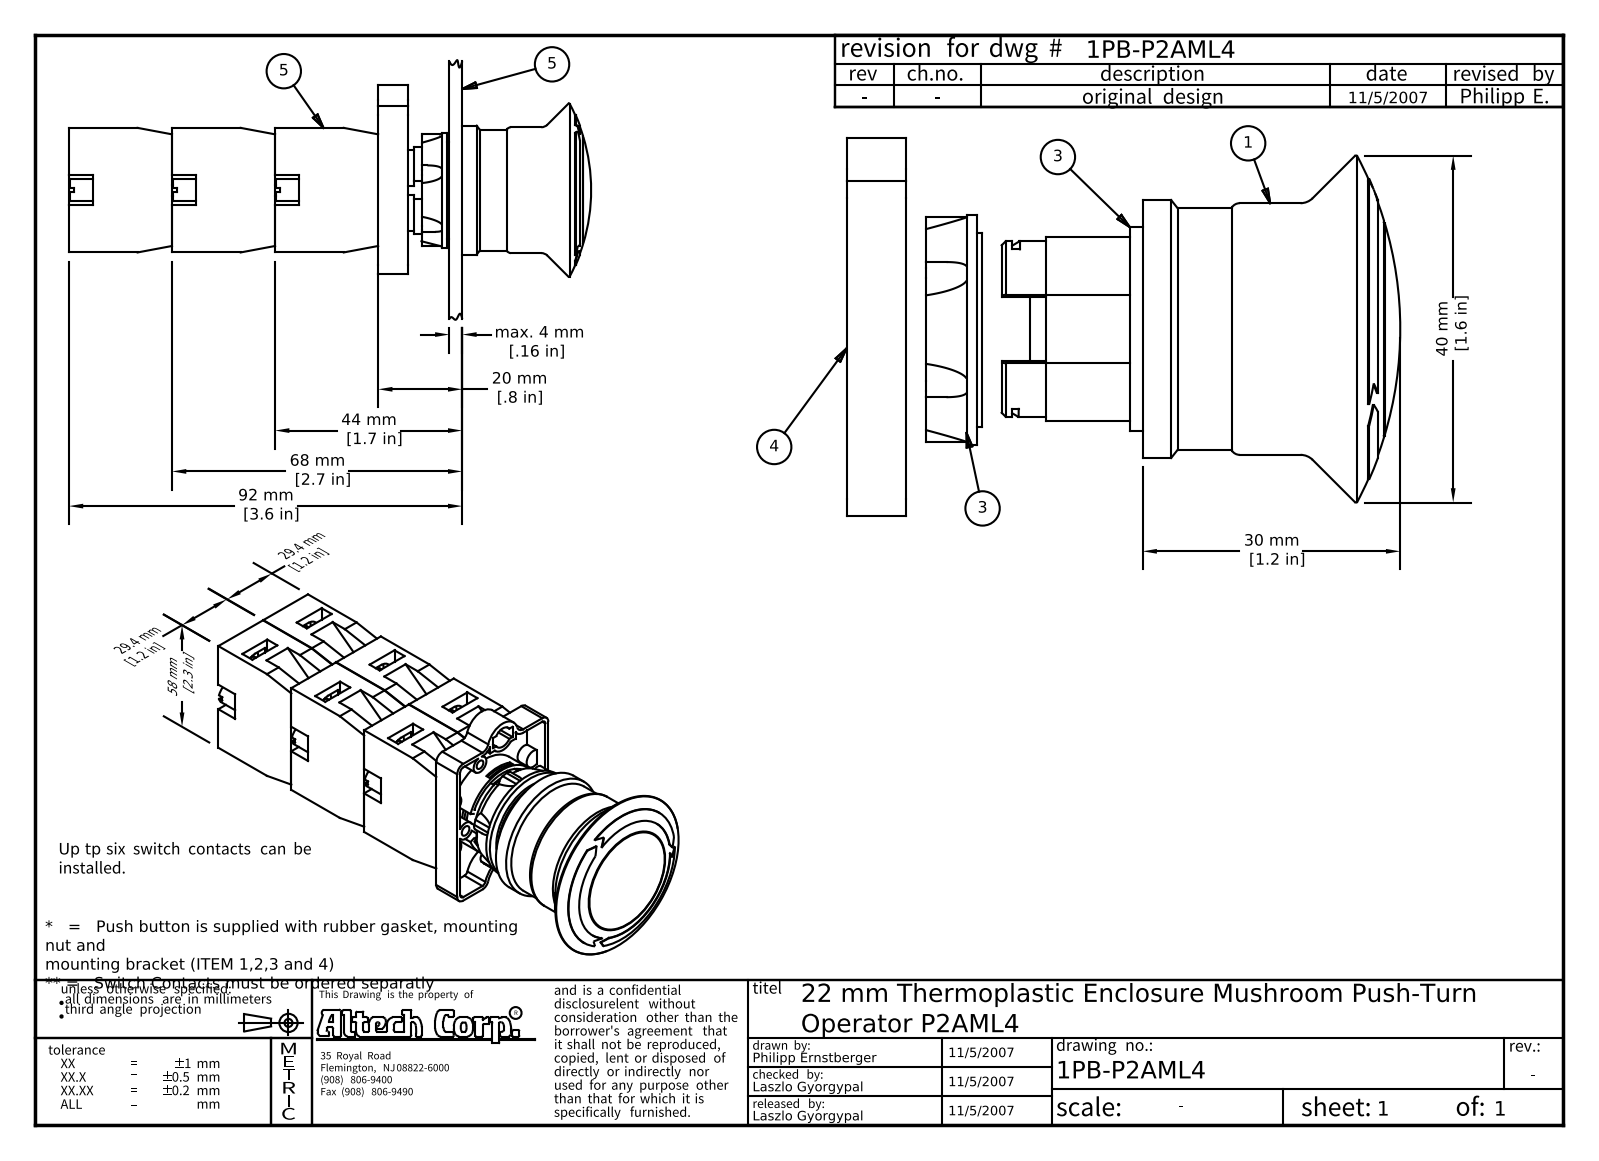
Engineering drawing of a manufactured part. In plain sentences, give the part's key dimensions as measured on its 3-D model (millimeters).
The part is named "P2AML4_assembly; P2AML4_operator; P2AML4; 2PRG1 (+7 more)". Its 3-D file was written by "Autodesk Inventor 2008 (AUTOMOTIVE_DESIGN)". It is 29 solids with 1183 faces: 639 planar, 203 cylindrical and 341 other. Overall it measures 119.6 by 60.45 by 45 millimeters. Its volume is 88 144 cubic millimeters and its surface area 46 867 square millimeters. Round holes: 6 of diameter 2.5, 2 of diameter 2.2, 2 of diameter 2.6, 1 of diameter 17.6, 1 of diameter 20.8, 1 of diameter 22.5, 1 of diameter 28.3, 1 of diameter 30. Round bosses or shafts: 6 of diameter 3, 4 of diameter 2.75, 4 of diameter 1.5, 2 of diameter 5, 2 of diameter 4.2, 1 of diameter 35, 1 of diameter 29.3, 1 of diameter 28.1. Partial cylindrical surfaces (rounded edges, fillets, slot ends): 15 of radius 1, 12 of radius 1.5, 8 of radius 2, 6 of radius 2.25, 2 of radius 3, 2 of radius 3.3, 2 of radius 5, 1 of radius 2.6. The main face-to-face distances are 14.8, 14.7, 24, 3, 48, 29.5, 14.6, 17.6, 29, 62.6. The hole center spacings are 6.54, 26.07, 11.41, 13, 14.49, 14.58, 17.17, 22.81.
